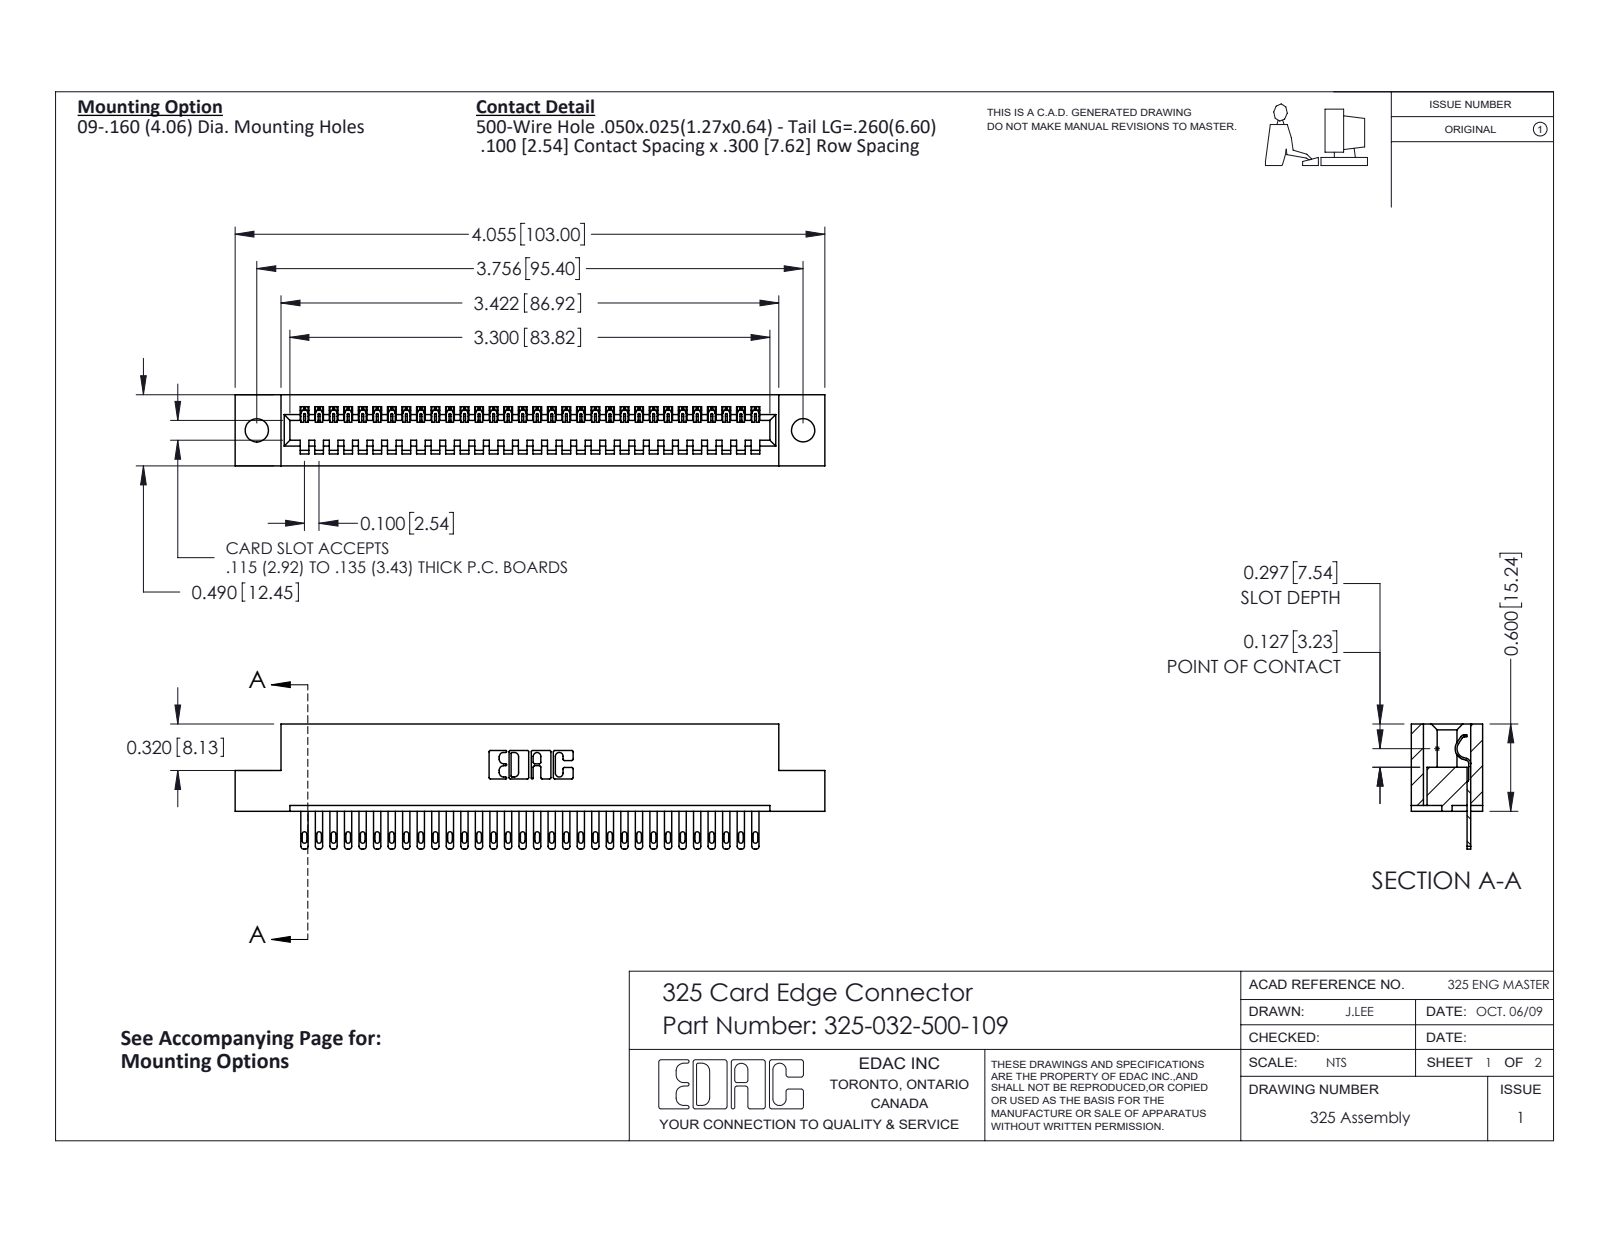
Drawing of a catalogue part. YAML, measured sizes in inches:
part_name: "325-032-500-109; 325 Part_.160 TH; 325-292-001_325-293-100"
step_written_by: "SolidWorks 2016 (CONFIG_CONTROL_DESIGN)"
units: inches
bodies: {solids: 33, faces: 1842, planar: 1222, cylindrical: 620, other: 0}
overall_size: [4.055, 0.86, 0.49]
volume: 0.78
surface_area: 21.34
round_holes:
  - {diameter: 0.16, count: 2}
partial_cylinders:
  - {radius: 0.006, count: 64}
  - {radius: 0.016, count: 64}
  - {radius: 0.02, count: 64}
  - {radius: 0.01, count: 22}
  - {radius: 0.007, count: 6}
  - {radius: 0.031, count: 6}
  - {radius: 0.026, count: 3}
  - {radius: 0.014, count: 1}
face_to_face_distances: [0.083, 0.407, 0.3, 0.49, 0.107, 0.383, 0.025, 0.325, 0.04, 0.1]
hole_center_spacings: [3.756]
